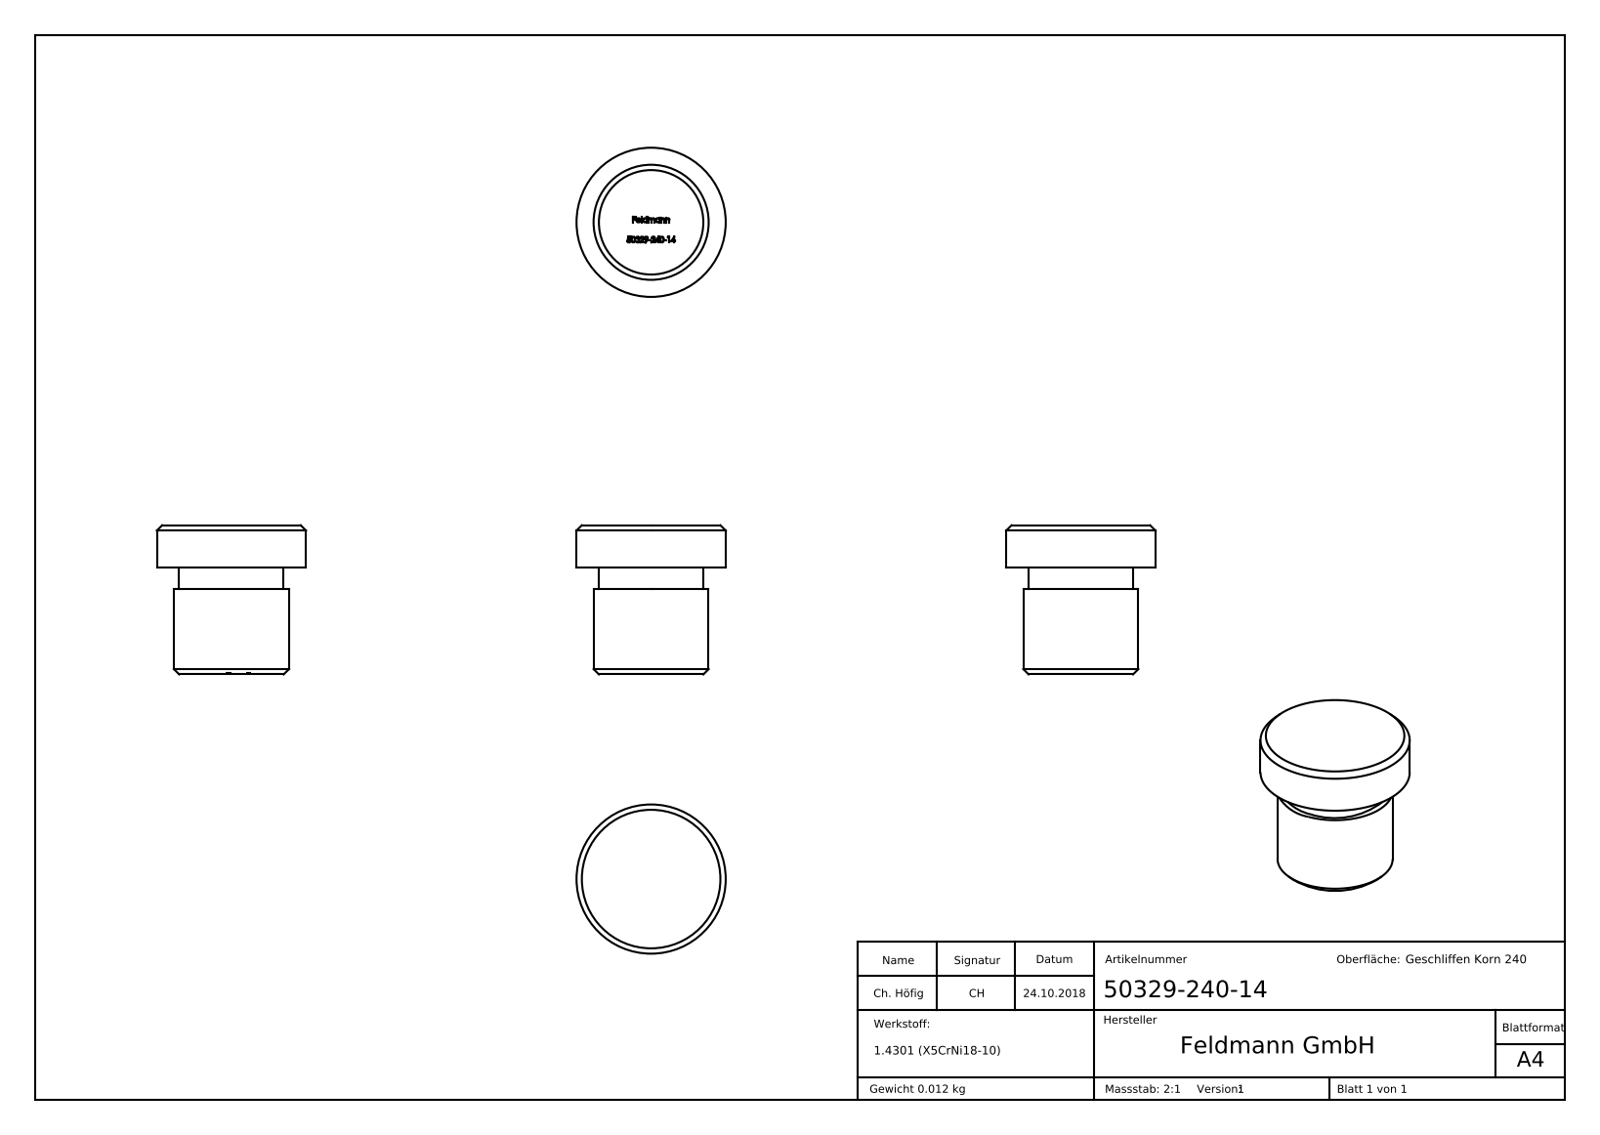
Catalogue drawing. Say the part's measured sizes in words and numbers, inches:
The part is named "50329-240-14". Its 3-D file was written by "SolidWorks 2015 (CONFIG_CONTROL_DESIGN)". It is 1 solid with 269 faces: 150 planar, 6 cylindrical and 113 other. Overall it measures 0.551 by 0.551 by 0.551 inches. Its volume is 0.091 cubic inches and its surface area 1.29 square inches. Round bosses or shafts: 1 of diameter 0.551, 1 of diameter 0.425, 1 of diameter 0.386. The main face-to-face distances are 0.157, 0.394, 0.551, 0.079, 0.315, 0.236, 0.311, 0.39, 0.547, 0.028.
